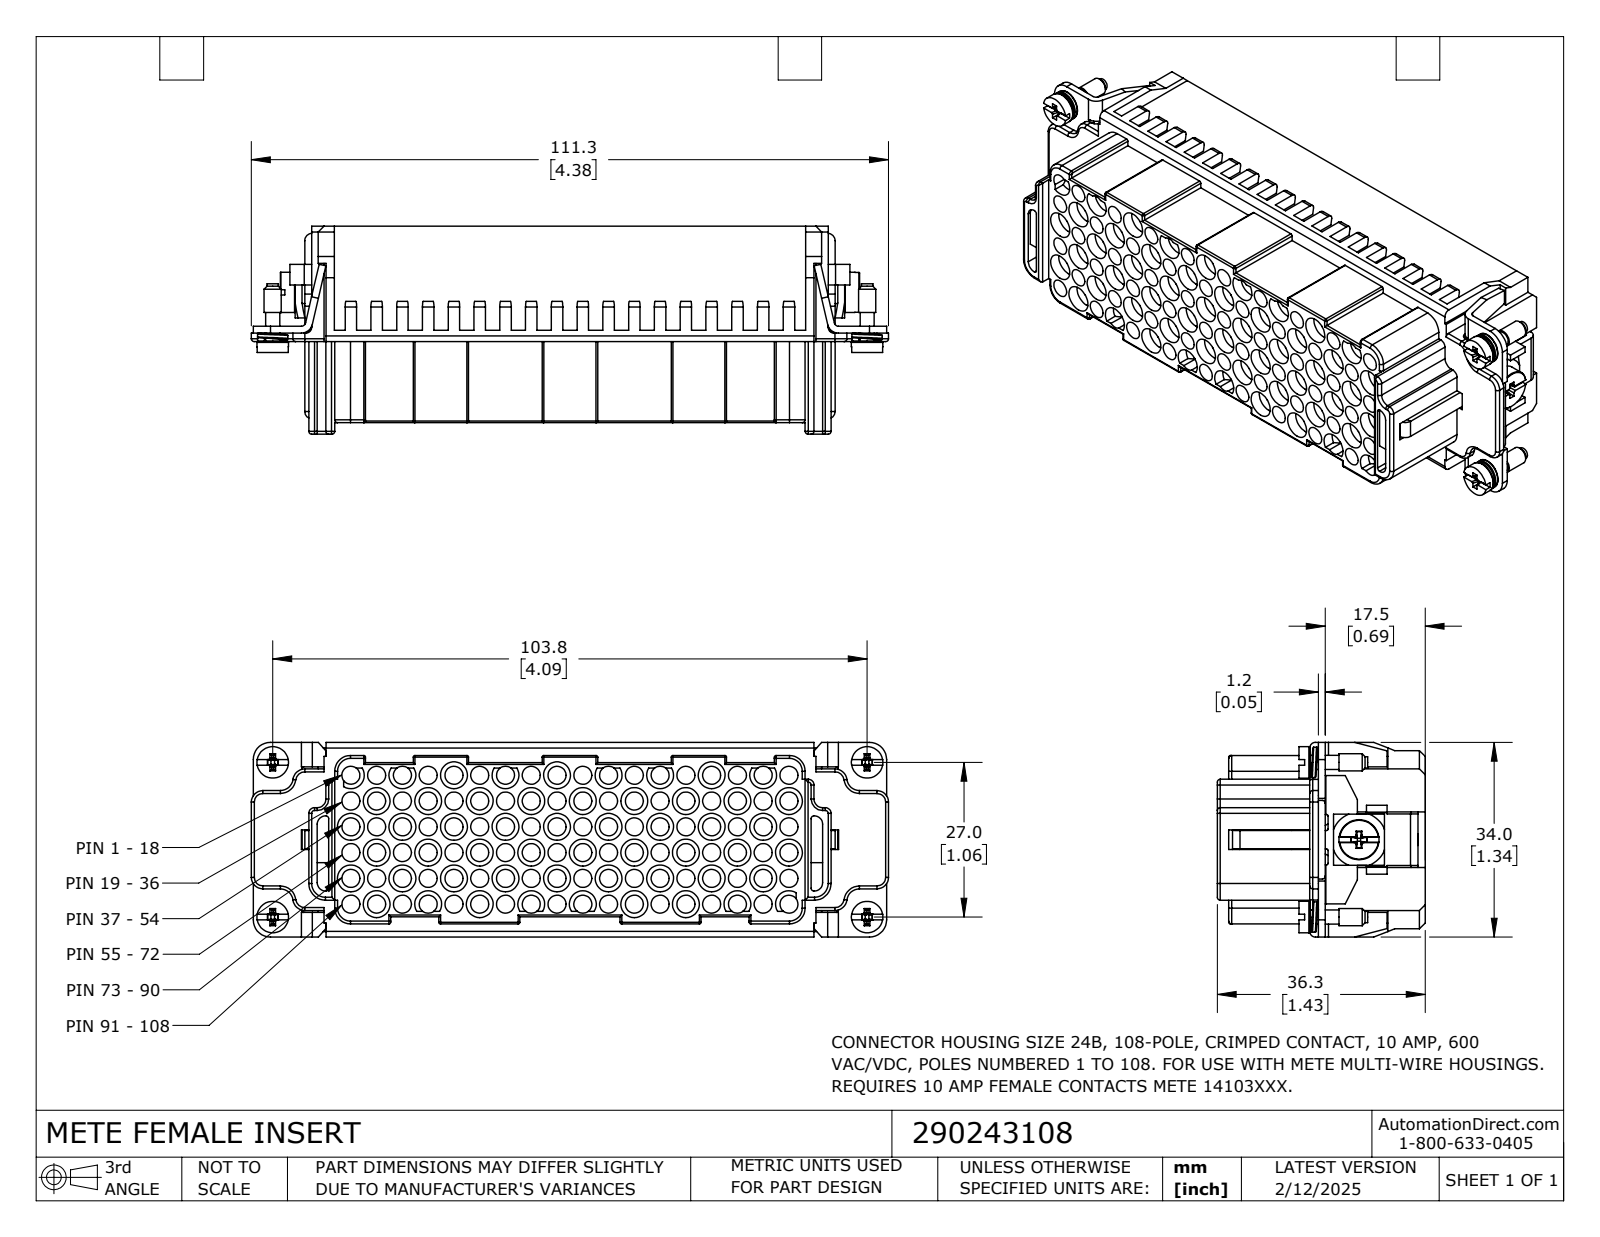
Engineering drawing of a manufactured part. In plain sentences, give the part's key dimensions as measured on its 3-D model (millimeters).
The part is named "290243108". Its 3-D file was written by "SolidWorks 2024 (CONFIG_CONTROL_DESIGN)". It is 15 solids with 1700 faces: 831 planar, 649 cylindrical and 220 other. Overall it measures 111.3 by 36.3 by 34 millimeters. Its volume is 78 150 cubic millimeters and its surface area 38 780 square millimeters. Round holes: 108 of diameter 3.1, 43 of diameter 4.7, 4 of diameter 2.9, 2 of diameter 3.6, 1 of diameter 3.3. Round bosses or shafts: 4 of diameter 5.5, 4 of diameter 5.3, 4 of diameter 3, 4 of diameter 2.4, 4 of diameter 2, 2 of diameter 3.2, 1 of diameter 7, 1 of diameter 5.1. Partial cylindrical surfaces (rounded edges, fillets, slot ends): 44 of radius 0.3, 32 of radius 0.3, 25 of radius 0.5, 11 of radius 2.4, 10 of radius 0.1, 10 of radius 1, 10 of radius 1.3, 8 of radius 0.4. The main face-to-face distances are 20.1, 29.1, 1.2, 1.1, 2.2, 28, 28.1, 29.3, 1.2, 34.3. The hole center spacings are 6.4, 14.2, 9, 23, 31.8, 12.7, 40.7, 18.
